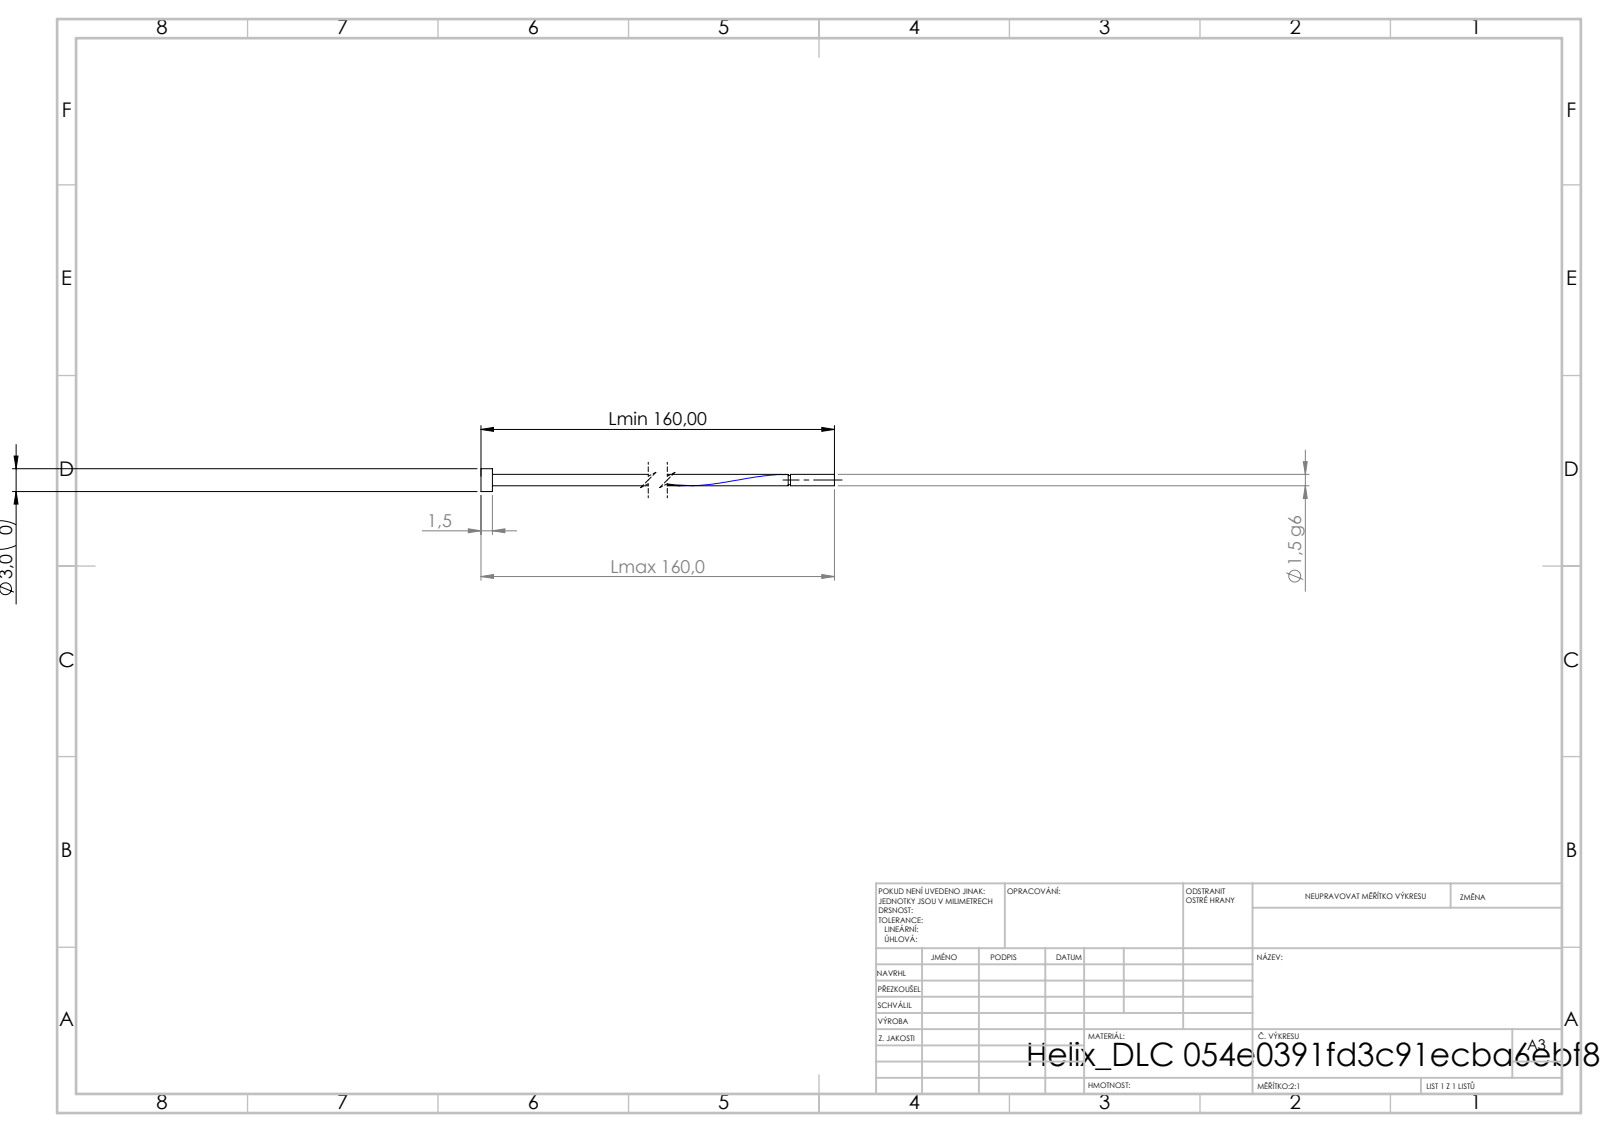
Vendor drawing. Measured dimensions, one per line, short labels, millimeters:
written by: SolidWorks 2019 (CONFIG_CONTROL_DESIGN)
unit: mm
bodies: 1 solid, 16 faces (6 planar, 9 cylindrical, 1 other)
size: 160 × 3 × 3
volume: 351 mm³; area: 1 039 mm²
bosses: 1× ⌀3, 1× ⌀1.5, 1× ⌀1.2
face distances: 1.5, 160, 158.5, 154.23, 152.73, 5.77, 153.93, 152.43, 6.07, 73.93
